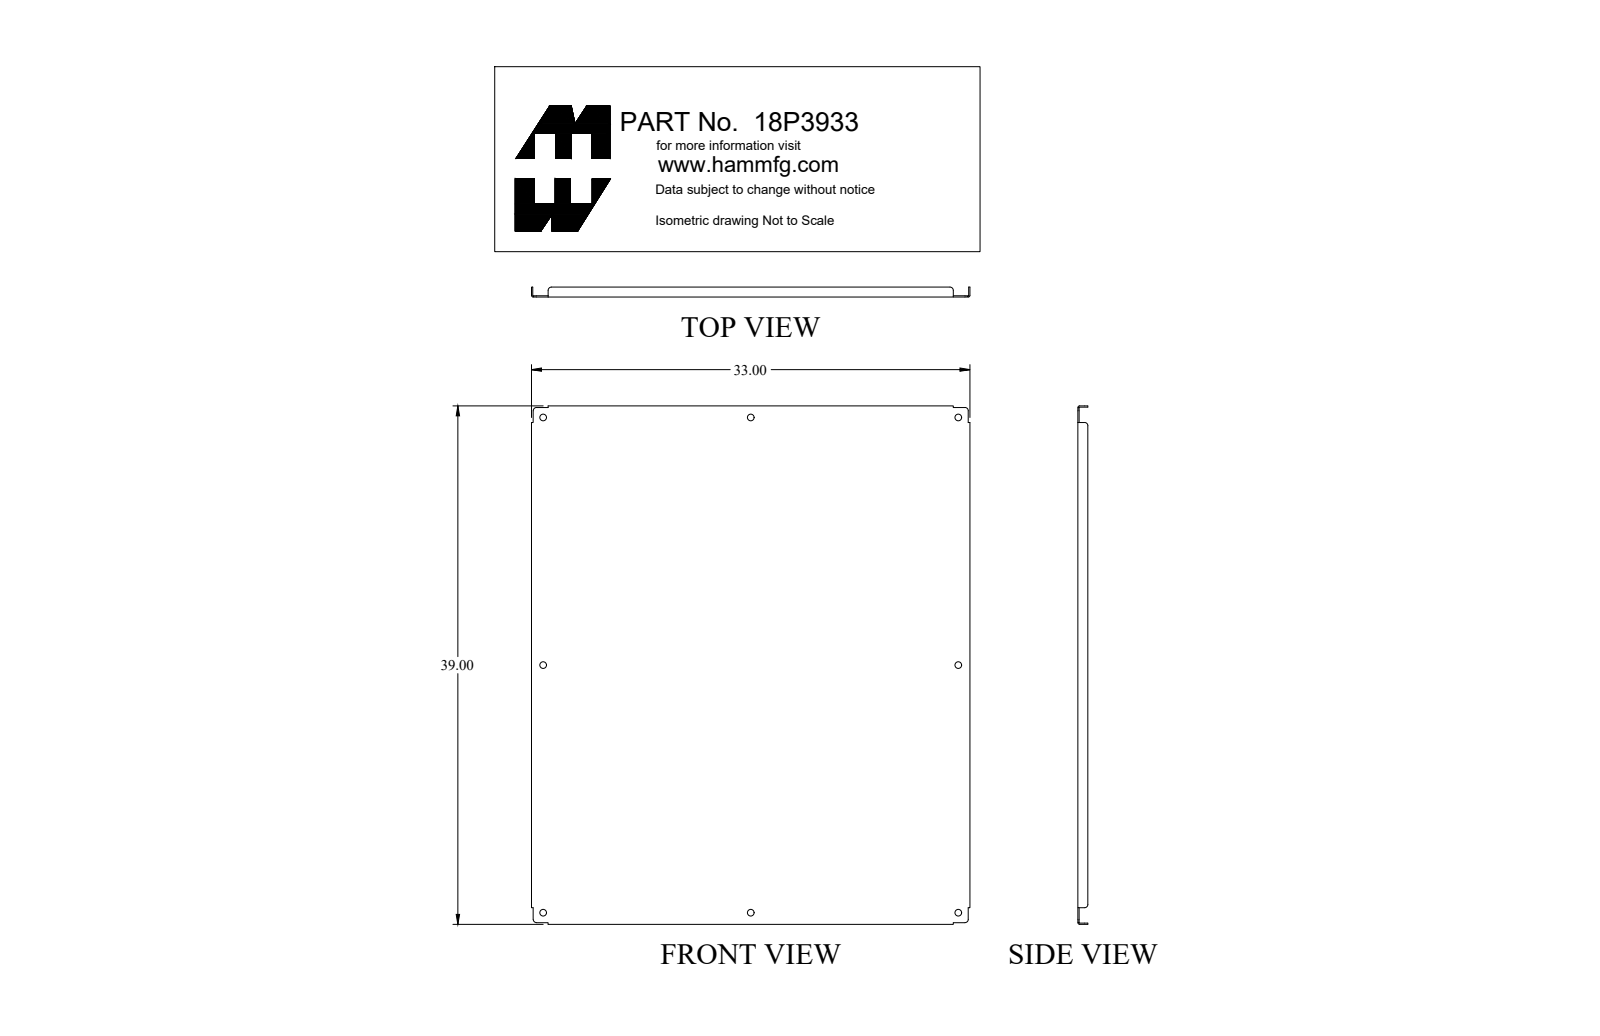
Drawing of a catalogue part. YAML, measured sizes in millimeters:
part_name: "18P3933_Default"
step_written_by: "SolidWorks 2018 (CONFIG_CONTROL_DESIGN)"
units: millimeters
bodies: {solids: 1, faces: 66, planar: 30, cylindrical: 36, other: 0}
overall_size: [990.6, 838.2, 19.1]
volume: 2129000
surface_area: 1774000
round_holes:
  - {diameter: 12.7, count: 8}
partial_cylinders:
  - {radius: 6.4, count: 8}
  - {radius: 0.8, count: 4}
  - {radius: 3.2, count: 4}
face_to_face_distances: [2.4, 835.8, 988.2, 838.2, 833.4, 990.6, 985.8, 19.1, 16.6, 3.2]
hole_center_spacings: [396.9, 473.1, 617.5, 924.1, 1026, 793.8, 946.2, 1235]
